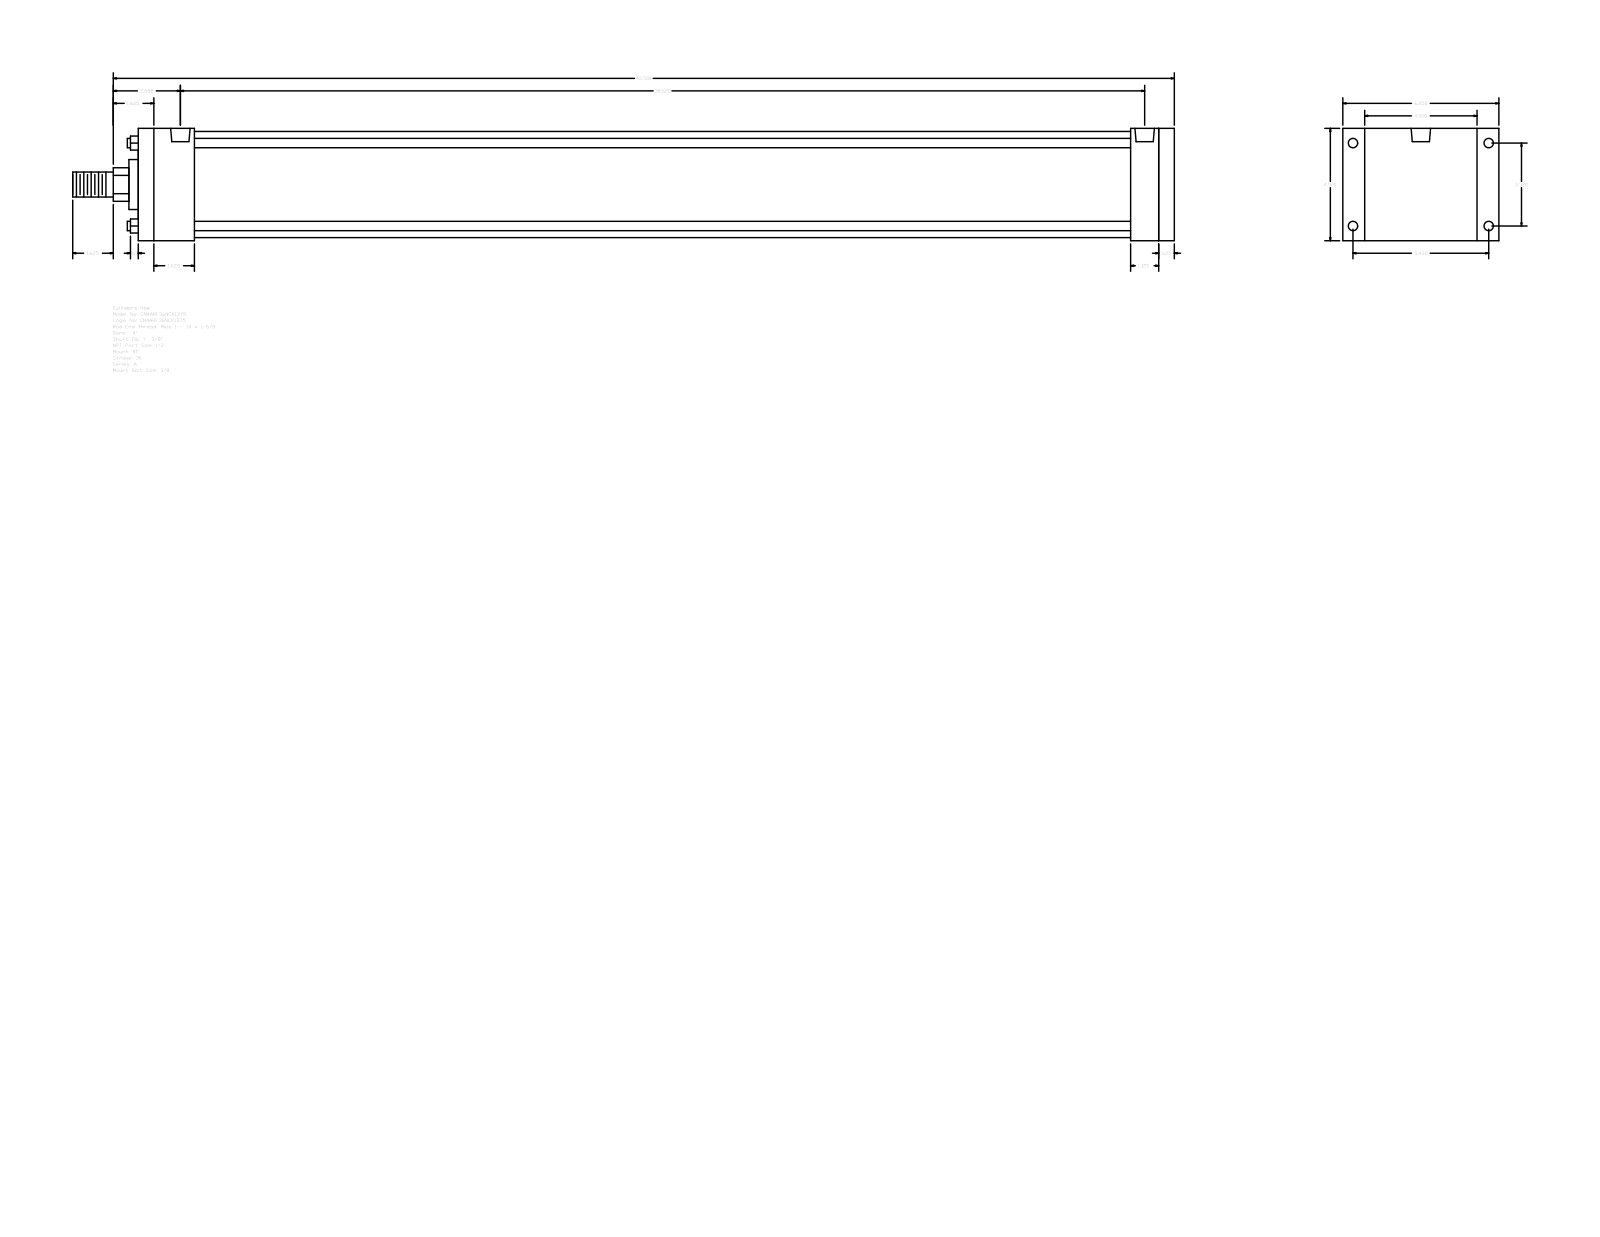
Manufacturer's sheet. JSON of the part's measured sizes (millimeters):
{"part_name": "A_RF__0400_1.375", "step_written_by": "GSSL Pune (CONFIG_CONTROL_DESIGN)", "units": "millimeters", "bodies": {"solids": 0, "faces": 92, "planar": 64, "cylindrical": 28, "other": 0}, "overall_size": [1120.78, 158.75, 114.3], "round_holes": [[8.73, 4], [9.53, 4], [19.77, 2]], "round_bosses_or_shafts": [[9.53, 4], [107.95, 1], [50.8, 1], [34.92, 1], [25.4, 1]], "partial_cylinders_radius": [[17.06, 1]], "face_to_face_distances": [114.3, 1054.1, 15.88, 1038.22, 57.15, 22.23, 136.53, 1009.65, 28.57, 44.45], "hole_center_spacings": [3.18, 84.32, 138.12, 161.82, 974.72, 977.9, 981.08]}
